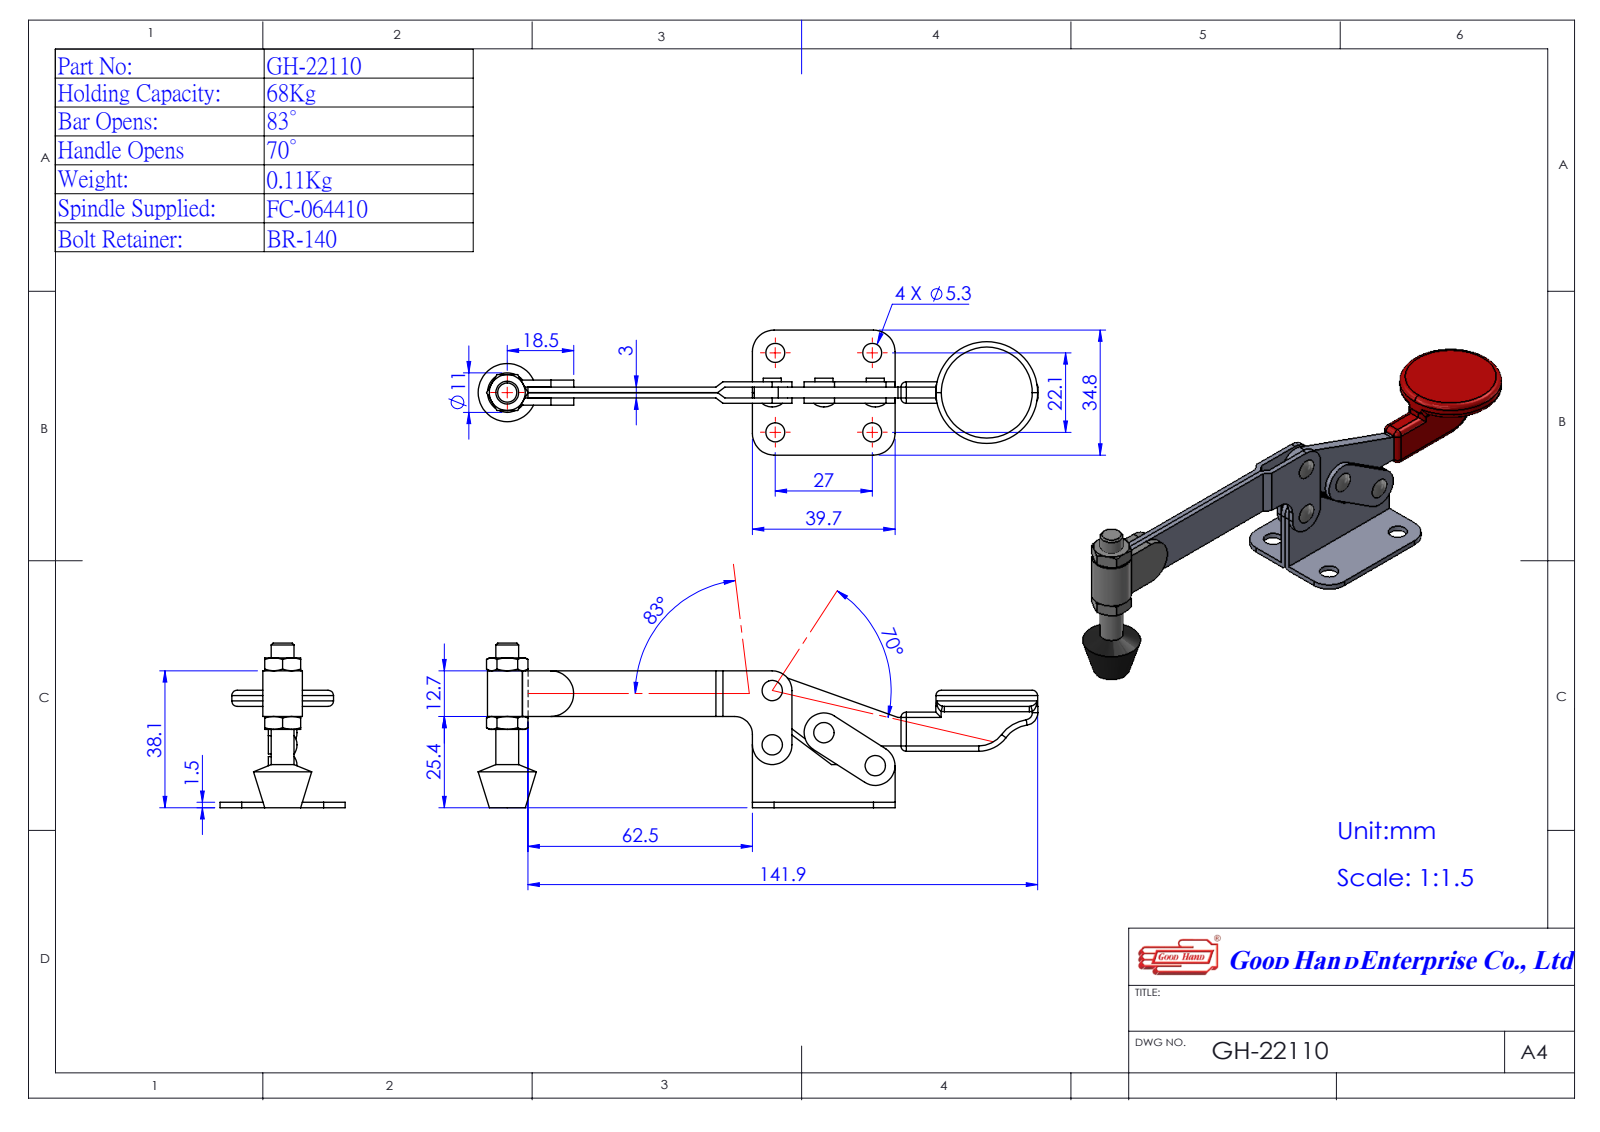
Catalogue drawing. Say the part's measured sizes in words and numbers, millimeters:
The part is named "12210001-1^GH-22110(簡化); GH-22110(簡化); Group4^GH-22110(簡化); Group2^GH-22110(簡化) (+2 more)". Its 3-D file was written by "SolidWorks 2016 (AUTOMOTIVE_DESIGN)". It is 5 solids with 244 faces: 106 planar, 92 cylindrical and 46 other. Overall it measures 157.13 by 45.8 by 34.8 millimeters. Its volume is 18 762 cubic millimeters and its surface area 17 798 square millimeters. Round holes: 4 of diameter 3, 4 of diameter 5.3, 1 of diameter 5, 1 of diameter 6. Round bosses or shafts: 2 of diameter 5.05, 2 of diameter 4.05, 1 of diameter 28.32, 1 of diameter 6.35, 1 of diameter 3. Partial cylindrical surfaces (rounded edges, fillets, slot ends): 6 of radius 5.5, 4 of radius 6, 2 of radius 2.02, 2 of radius 3.5, 2 of radius 5, 1 of radius 4.5, 1 of radius 6.35, 1 of radius 9.13. The main face-to-face distances are 1.5, 3, 4.5, 6, 2, 3.5, 5, 6.5, 0.5, 37.78. The hole center spacings are 22.1, 27, 34.89, 76.75, 103.54, 14.77, 14.78, 17.
